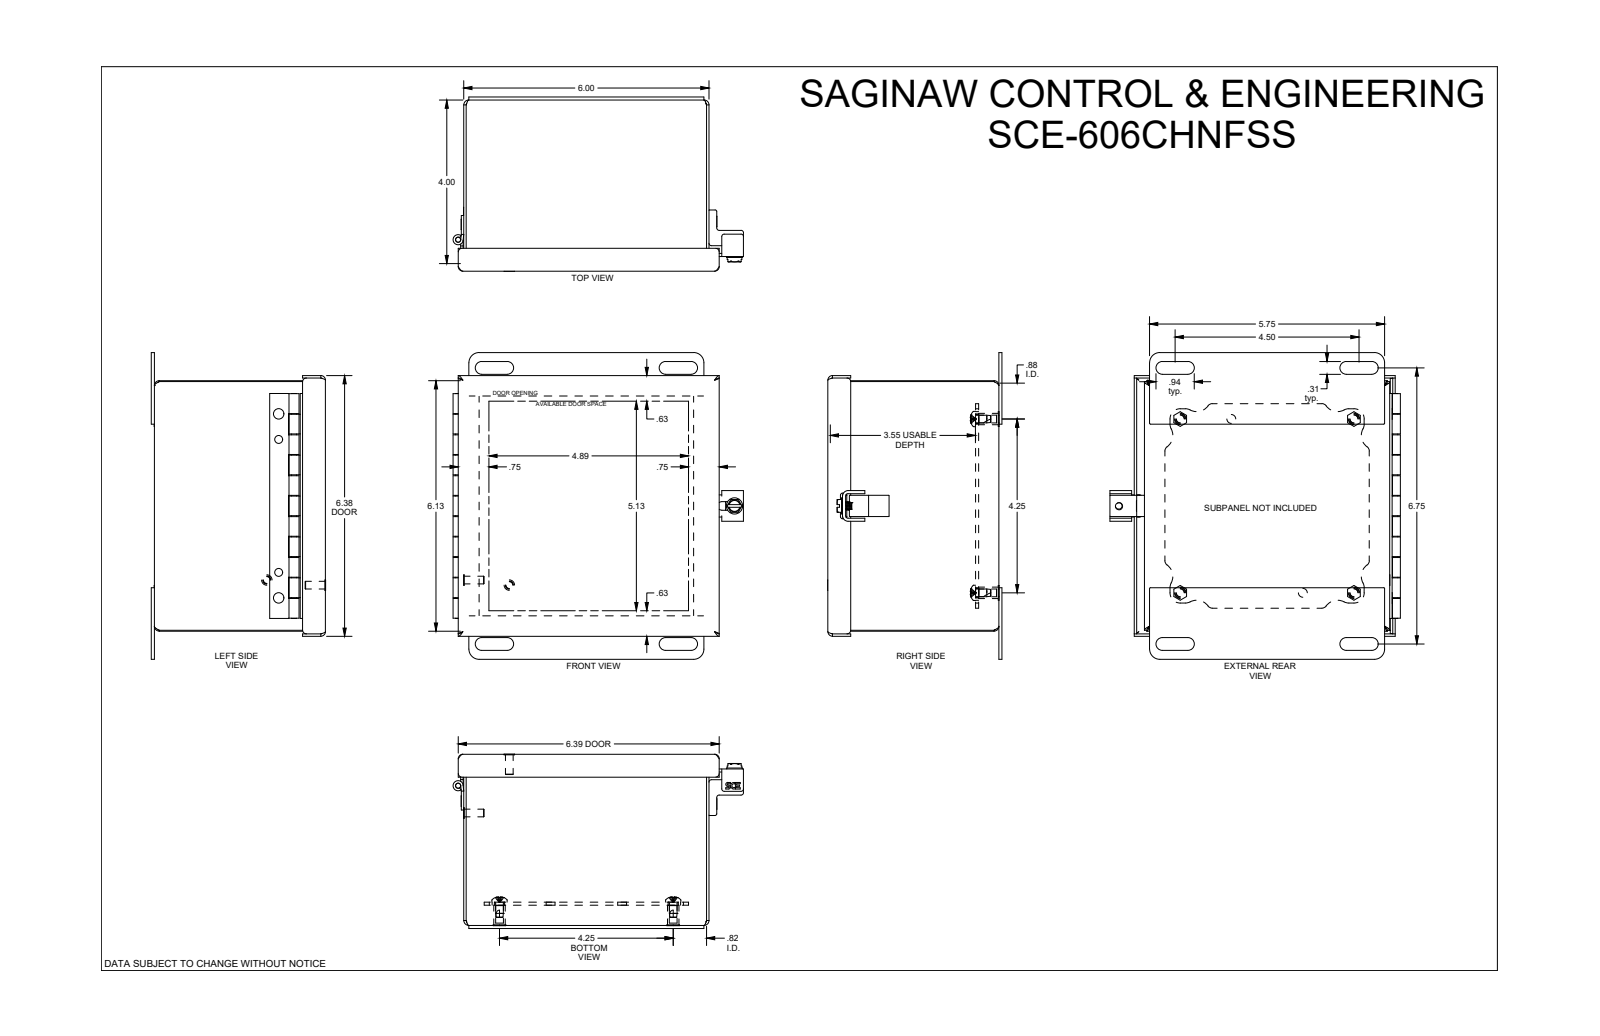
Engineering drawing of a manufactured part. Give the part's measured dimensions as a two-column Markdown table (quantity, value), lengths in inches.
| quantity | value |
| --- | --- |
| part name | SCE-606CHNFSS |
| STEP written by | SolidWorks 2019 (CONFIG_CONTROL_DESIGN) |
| units | inches |
| bodies | 0 solids, 1010 faces (467 planar, 275 cylindrical, 268 other) |
| overall size | 7.5 × 7.104 × 4.265 |
| round holes (diameter × count) | 0.19 × 7, 0.193 × 5, 0.25 × 4, 0.281 × 4, 0.193 × 2, 0.218 × 2, 0.126 × 1, 0.156 × 1, 0.266 × 1 |
| round bosses / shafts (diameter × count) | 0.188 × 10, 0.256 × 5, 0.373 × 4, 0.28 × 4, 0.396 × 1, 0.246 × 1, 0.123 × 1 |
| partial cylindrical surfaces (radius × count) | 0.01 × 42, 0.06 × 17, 0.25 × 16, 0.007 × 8, 0.052 × 8, 0.112 × 8, 0.125 × 8, 0.156 × 8 |
| main face-to-face distances | 0.06, 5.94, 4.125, 6.065, 0.06, 4.185, 4.125, 4.065, 0.075, 6 |
| hole center spacings | 4.25, 1.25, 2.251, 3, 4.43, 5.202, 6.01, 0.305 |
